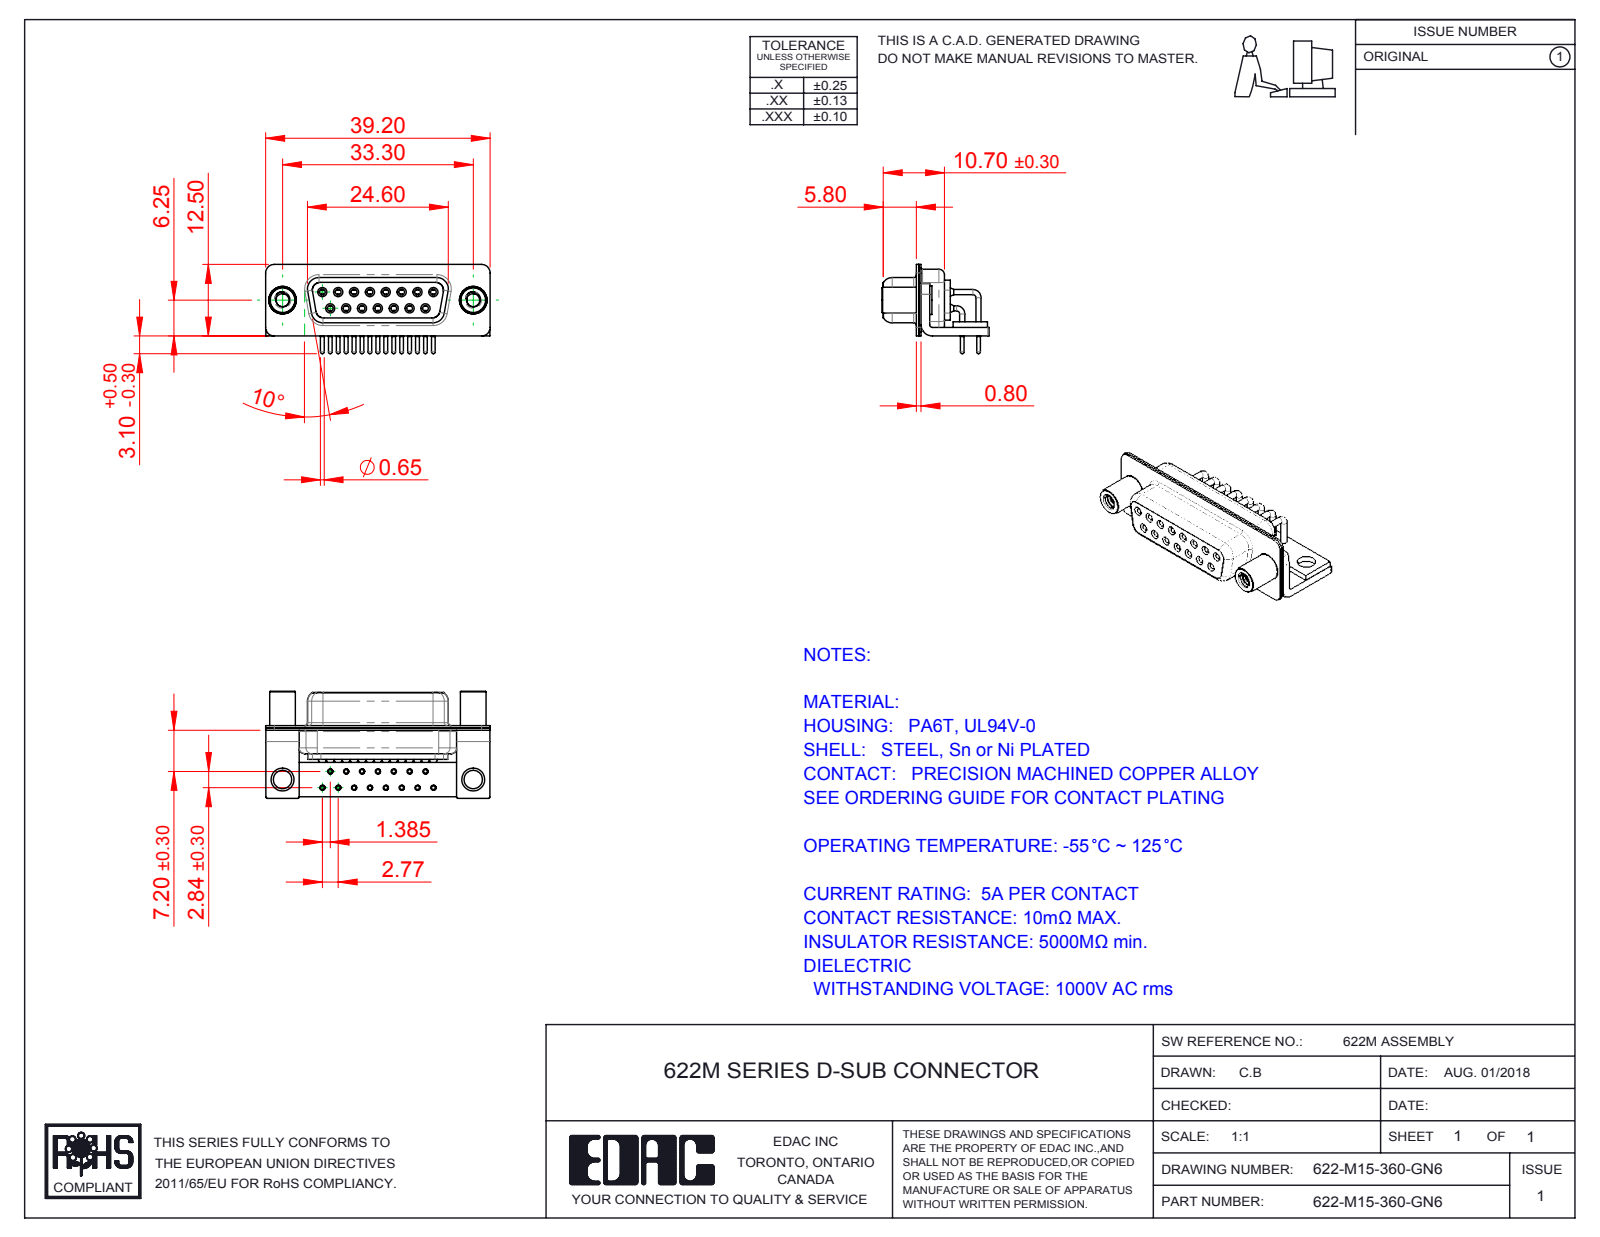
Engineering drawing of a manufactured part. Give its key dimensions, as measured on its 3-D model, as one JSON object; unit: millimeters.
{"part_name": "622M 4-40 Threaded Standoff; 622-M15-360-GN6; 622M Stabilizer Bracket; 622M Contact Row 2 (+5 more)", "step_written_by": "SolidWorks 2016 (CONFIG_CONTROL_DESIGN)", "units": "millimeters", "bodies": {"solids": 23, "faces": 1204, "planar": 320, "cylindrical": 576, "other": 308}, "overall_size": [39.2, 18.7, 15.6], "volume_mm3": 3100, "surface_area_mm2": 7827, "round_holes": [[0.9, 15], [1, 15], [1.1, 15], [1.7, 15], [1.8, 15], [2, 15], [2.26, 2], [3.2, 2], [4, 2], [4.8, 2]], "round_bosses_or_shafts": [[0.9, 22], [1.6, 15], [1.5, 15], [0.65, 15], [5, 2], [4.9, 2], [4.5, 2]], "partial_cylinders_radius": [[0.25, 16], [1.5, 16], [2, 13], [1.35, 8], [1.6, 8], [0.5, 5], [0.6, 4], [0.65, 4]], "face_to_face_distances": [0.4, 2.3, 1.9, 0.8, 9.35, 1.5, 1, 1.45, 8.95, 0.85], "hole_center_spacings": [3.16, 2.77, 5.54, 8.31, 11.08, 5.03, 5.04, 7.48]}
